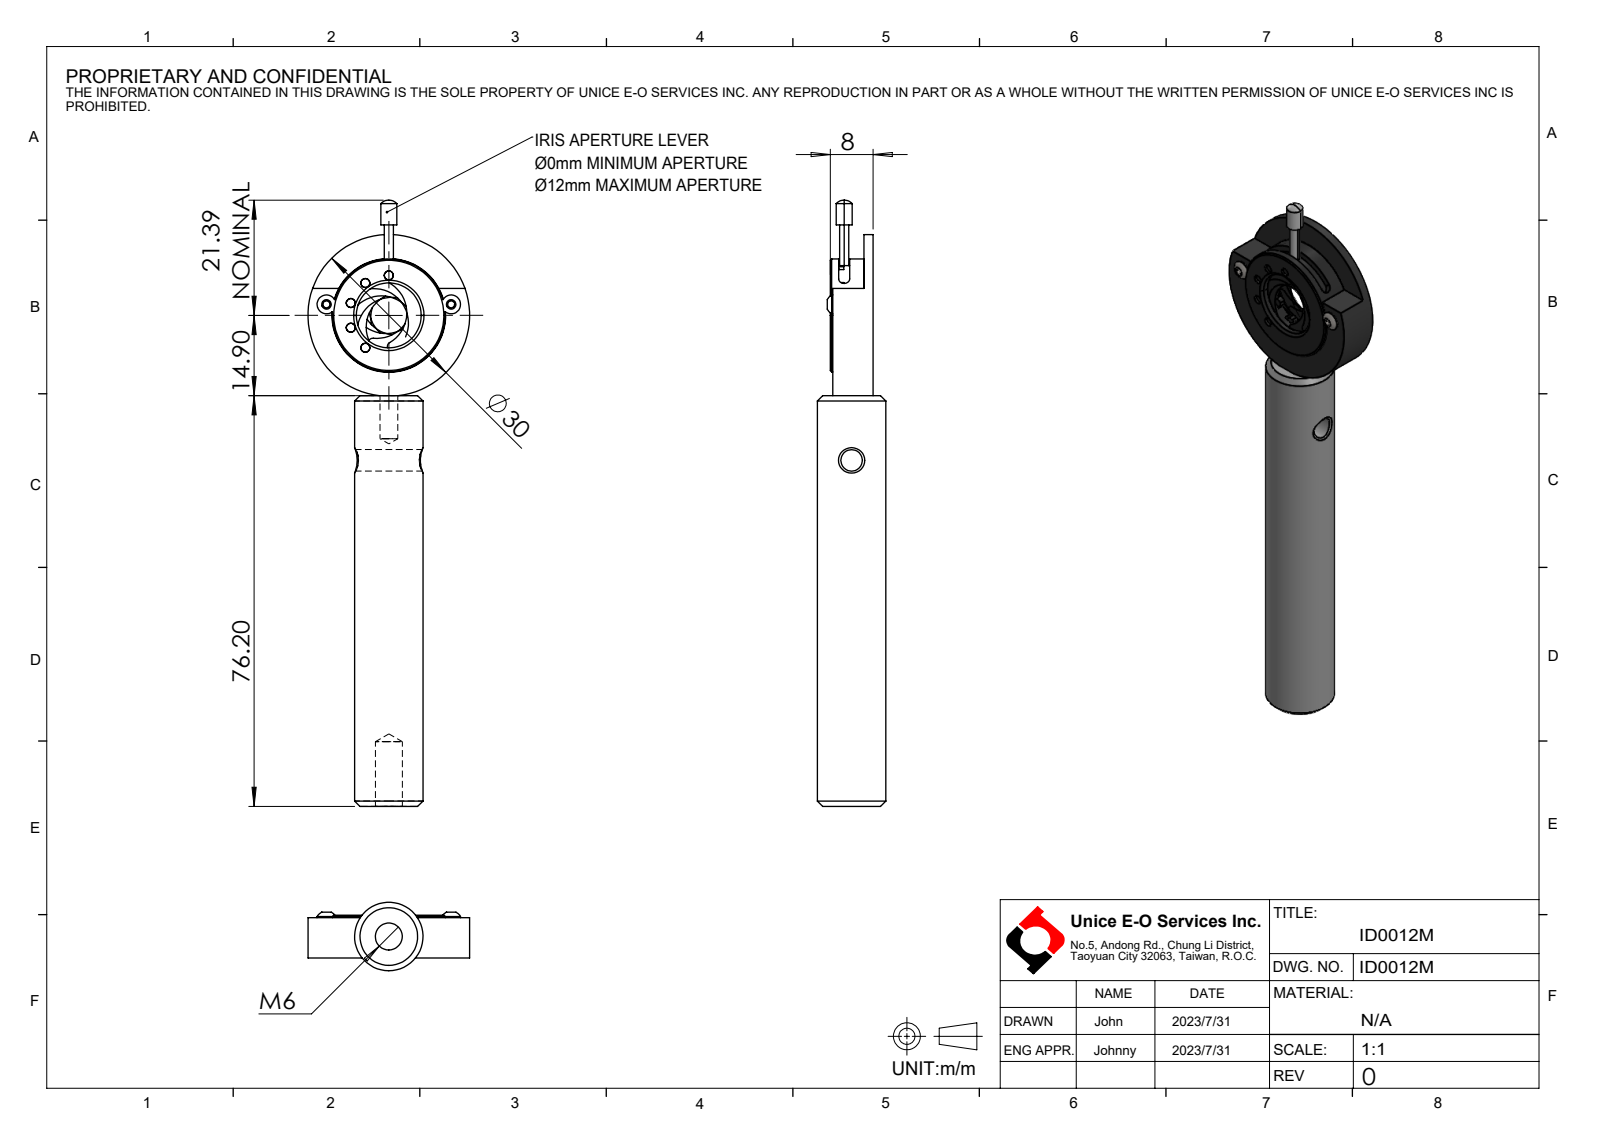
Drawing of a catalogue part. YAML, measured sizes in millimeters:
part_name: "ID0012M"
step_written_by: "SolidWorks 2022 (CONFIG_CONTROL_DESIGN)"
units: millimeters
bodies: {solids: 18, faces: 308, planar: 130, cylindrical: 162, other: 16}
overall_size: [112.48, 30, 12.7]
volume: 12579
surface_area: 9553
round_holes:
  - {diameter: 1.68, count: 5}
  - {diameter: 1.7, count: 5}
  - {diameter: 1.6, count: 2}
  - {diameter: 1.25, count: 1}
  - {diameter: 3.3, count: 1}
  - {diameter: 4, count: 1}
  - {diameter: 5, count: 1}
  - {diameter: 12.04, count: 1}
  - {diameter: 12.12, count: 1}
  - {diameter: 12.62, count: 1}
  - {diameter: 15, count: 1}
  - {diameter: 18.63, count: 1}
round_bosses_or_shafts:
  - {diameter: 1.52, count: 10}
  - {diameter: 1.65, count: 6}
  - {diameter: 1.65, count: 5}
  - {diameter: 3.5, count: 2}
  - {diameter: 2, count: 2}
  - {diameter: 30, count: 1}
  - {diameter: 20.96, count: 1}
  - {diameter: 20.32, count: 1}
partial_cylinders:
  - {radius: 0.83, count: 10}
  - {radius: 0.85, count: 10}
  - {radius: 1.61, count: 10}
  - {radius: 6.38, count: 10}
  - {radius: 9.6, count: 10}
  - {radius: 1.03, count: 2}
face_to_face_distances: [3.21, 1.5, 1.09, 3.02, 1.52, 3.13, 3.18, 3.26, 3.24, 3.29]
hole_center_spacings: [14.06, 7.37, 11.96, 8.69, 14.78, 4.55, 4.57, 4.58]
